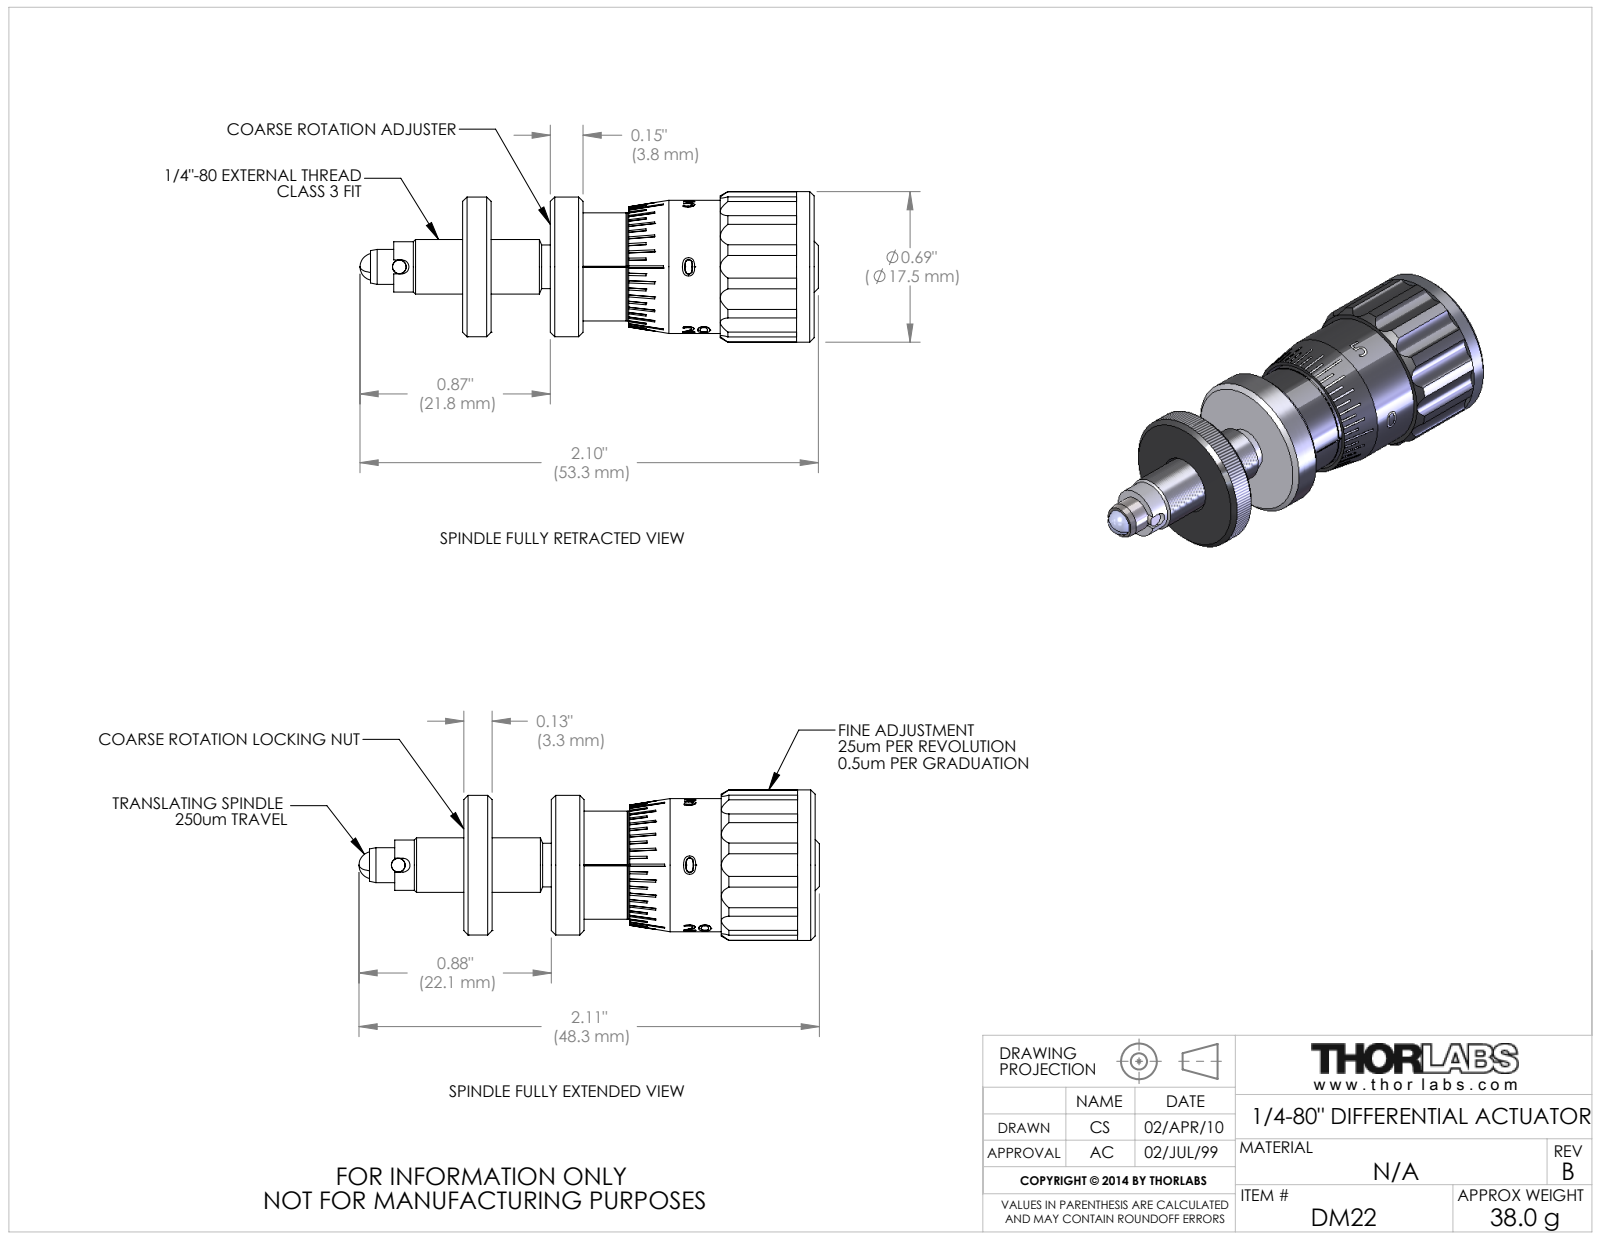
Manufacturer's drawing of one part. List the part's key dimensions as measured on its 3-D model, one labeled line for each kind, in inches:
Part name (STEP PRODUCT): 1578-E0W
STEP written by: SolidWorks 2012 (AUTOMOTIVE_DESIGN)
Units: inches
Bodies: 11 solids, 562 faces (252 planar, 128 cylindrical, 182 other)
Overall size (bounding box): 2.101 × 0.69 × 0.69
Volume: 0.362 in³ · Surface area: 11.84 in²
Round holes (diameter × count): ⌀0.063 ×1, ⌀0.063 ×1, ⌀0.106 ×1, ⌀0.125 ×1, ⌀0.138 ×1, ⌀0.138 ×1, ⌀0.14 ×1, ⌀0.16 ×1, ⌀0.17 ×1, ⌀0.187 ×1, ⌀0.236 ×1, ⌀0.24 ×1
Round bosses / shafts (diameter × count): ⌀0.69 ×1, ⌀0.64 ×1, ⌀0.61 ×1, ⌀0.495 ×1, ⌀0.494 ×1, ⌀0.44 ×1, ⌀0.338 ×1, ⌀0.335 ×1
Partial cylindrical surfaces — rounded edges, fillets, slot ends (radius × count): R0.094 ×14, R0.032 ×1, R0.306 ×1
Main face-to-face distances: 1.129, 0.08, 1.4, 0.272, 1.531, 0.402, 0.13, 0.285, 0.844, 1.115
